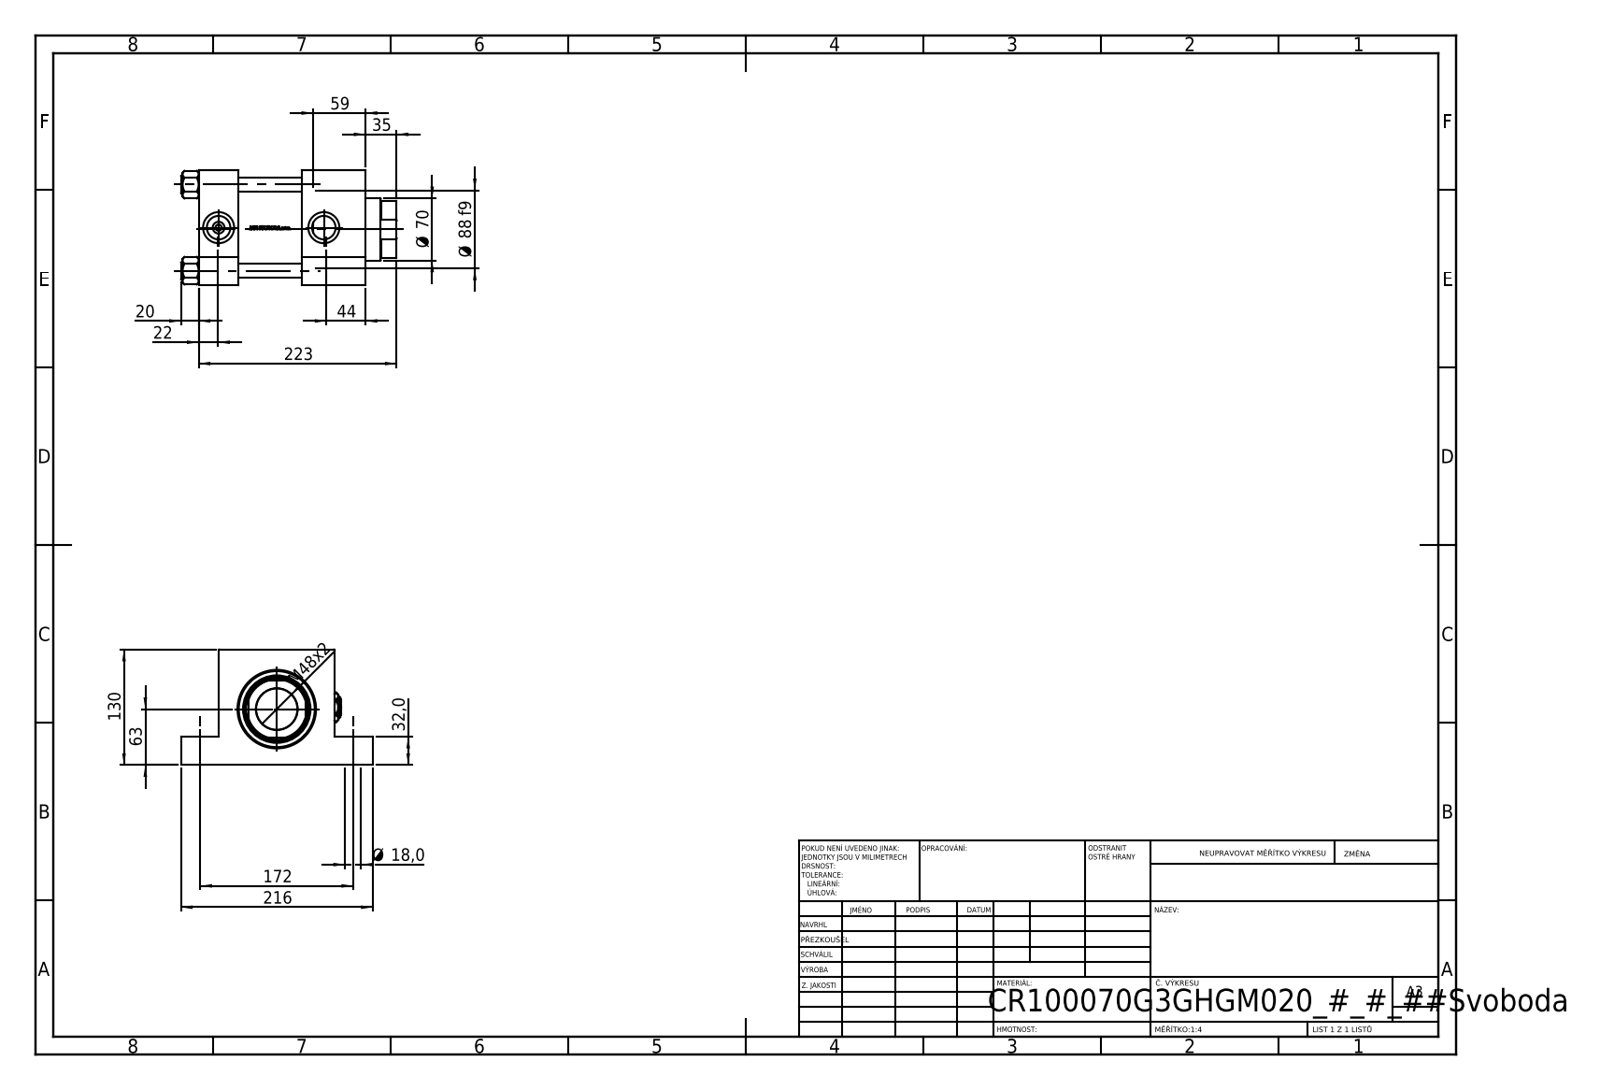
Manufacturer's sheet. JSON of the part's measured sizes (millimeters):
{"part_name": "V215CR_VCP_G; V215_VC_A; Zatka_pro_OIL_PORT; NUT_M5_G (+2 more)", "step_written_by": "SolidWorks 2019 (CONFIG_CONTROL_DESIGN)", "units": "millimeters", "bodies": {"solids": 13, "faces": 1231, "planar": 525, "cylindrical": 132, "other": 574}, "overall_size": [243, 216, 130], "volume_mm3": 2874000, "surface_area_mm2": 378787, "round_holes": [[16, 4], [18, 4], [7, 2], [26.44, 2], [35, 2], [46.5, 1], [70, 1], [73, 1], [76, 1], [85.5, 1], [100, 1]], "round_bosses_or_shafts": [[19, 4], [106, 1], [88, 1]], "partial_cylinders_radius": [[34, 1]], "face_to_face_distances": [130, 45, 116, 188, 143, 71, 72, 32, 98, 43], "hole_center_spacings": [96.9, 67.12, 69.95, 122, 137.04, 172, 210.87, 118.5]}
